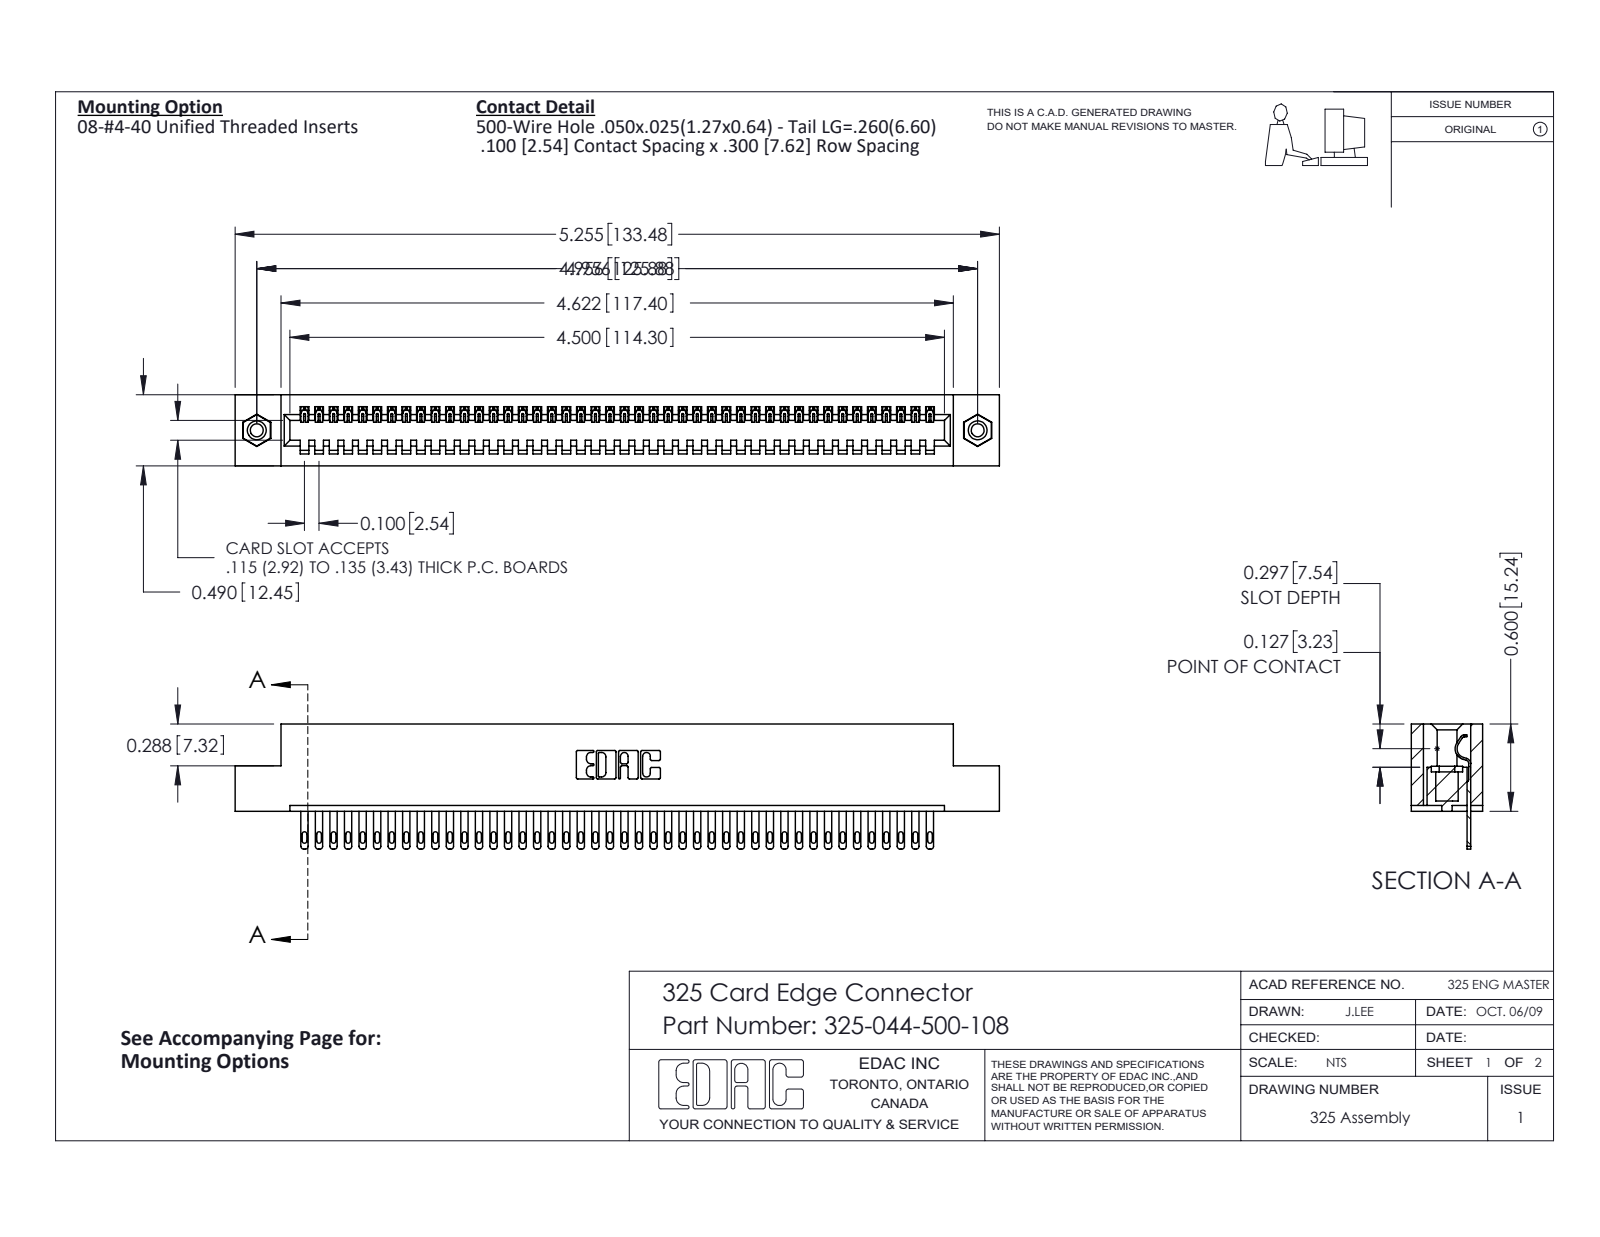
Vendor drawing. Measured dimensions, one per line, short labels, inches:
name: 325 Part_TI; 325-292-001_325-293-100; 325-044-500-108; 345-250-001_345-250-003-102
written by: SolidWorks 2016 (CONFIG_CONTROL_DESIGN)
unit: in
bodies: 47 solids, 2550 faces (1686 planar, 848 cylindrical, 16 other)
size: 5.255 × 0.86 × 0.49
volume: 1.036 in³; area: 28.99 in²
holes: 2× ⌀0.089, 2× ⌀0.125, 2× ⌀0.16
bosses: 2× ⌀0.155
rounds: 88× R0.006, 88× R0.016, 88× R0.02, 22× R0.01, 6× R0.007, 6× R0.031, 3× R0.026, 1× R0.014
face distances: 0.083, 0.407, 0.49, 0.3, 0.107, 0.383, 0.025, 0.325, 0.56, 0.04
hole spacings: 4.956
